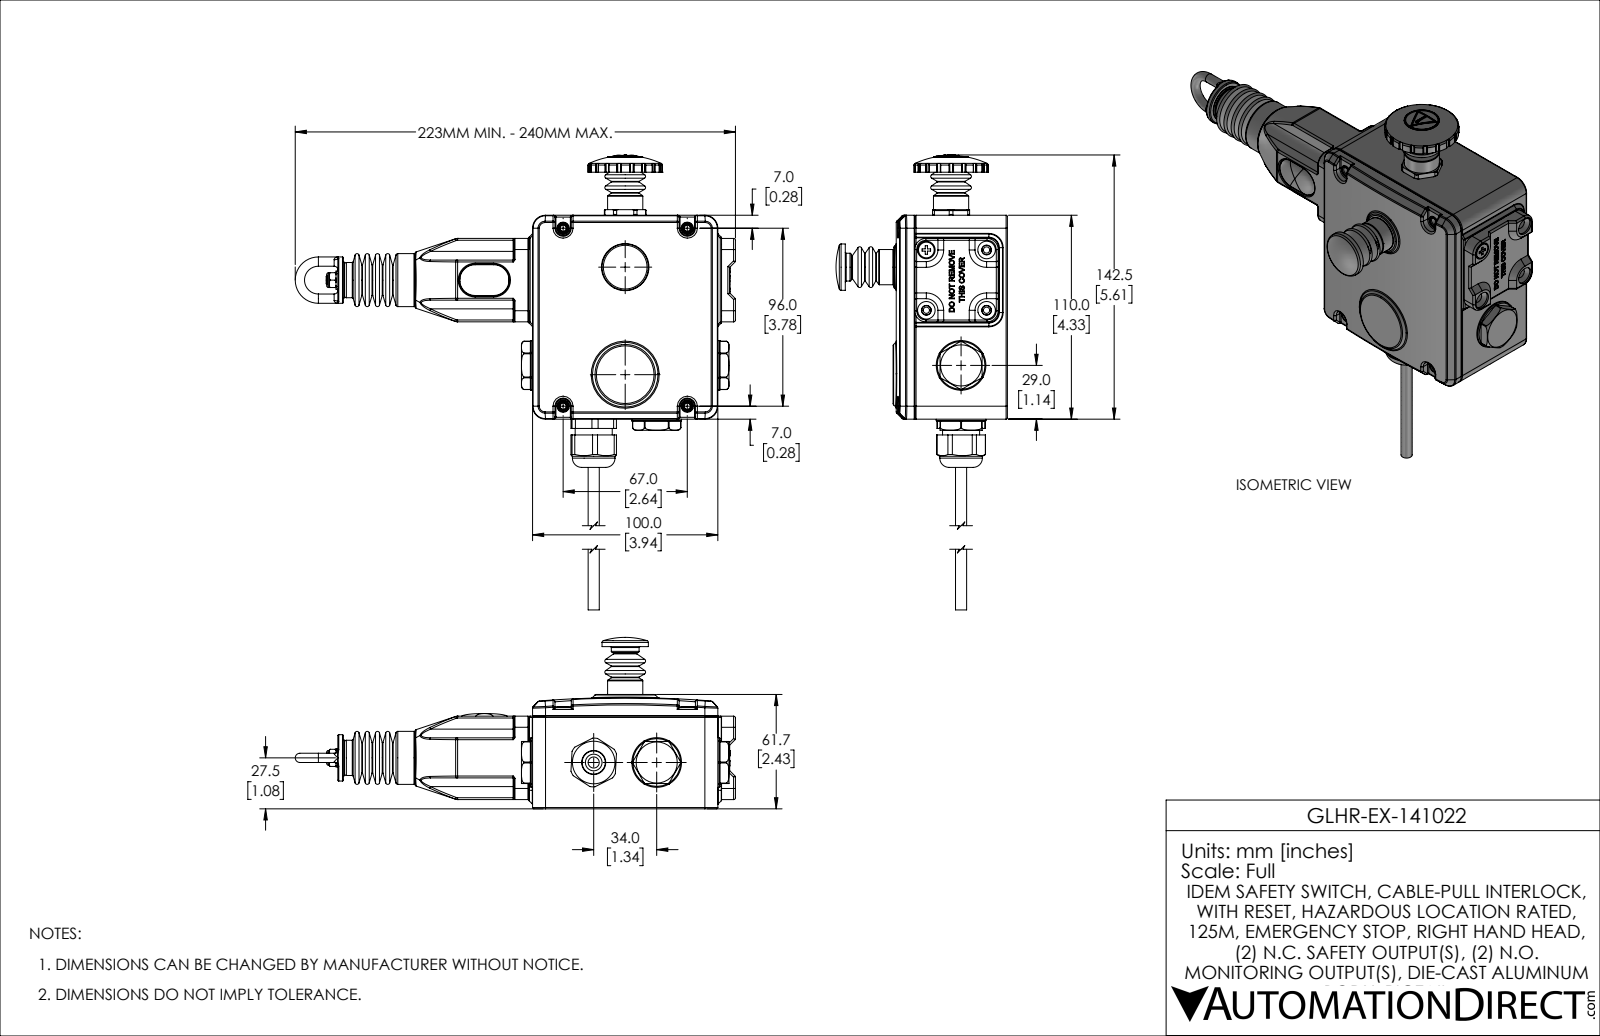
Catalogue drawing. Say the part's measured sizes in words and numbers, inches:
The part is named "GLHR-EX-141022". Its 3-D file was written by "SolidWorks 2021 (AUTOMOTIVE_DESIGN)". It is 27 solids with 3202 faces: 979 planar, 1029 cylindrical and 1194 other. Overall it measures 9.354 by 9.193 by 3.642 inches. Its volume is 18.11 cubic inches and its surface area 279.5 square inches. Round holes: 11 of diameter 0.197, 9 of diameter 0.209, 7 of diameter 0.354, 7 of diameter 0.374, 5 of diameter 0.138, 4 of diameter 0.13, 4 of diameter 0.157, 4 of diameter 0.189, 4 of diameter 0.213, 4 of diameter 0.228, 3 of diameter 0.118, 3 of diameter 0.173. Round bosses or shafts: 8 of diameter 0.236, 4 of diameter 0.335, 4 of diameter 0.173, 3 of diameter 0.748, 3 of diameter 0.197, 2 of diameter 1.055, 2 of diameter 0.984, 2 of diameter 0.764. Partial cylindrical surfaces (rounded edges, fillets, slot ends): 220 of radius 0.02, 137 of radius 0.039, 88 of radius 0.008, 64 of radius 0.028, 20 of radius 0.012, 14 of radius 0.006, 12 of radius 0.236, 11 of radius 0.004. The main face-to-face distances are 2.157, 0.138, 2.043, 0.114, 4.331, 0.079, 0.157, 0.055, 3.878, 4.016. The hole center spacings are 1.28, 1.28, 0.374, 0.905, 1.891, 1.913, 3.012, 3.489.
